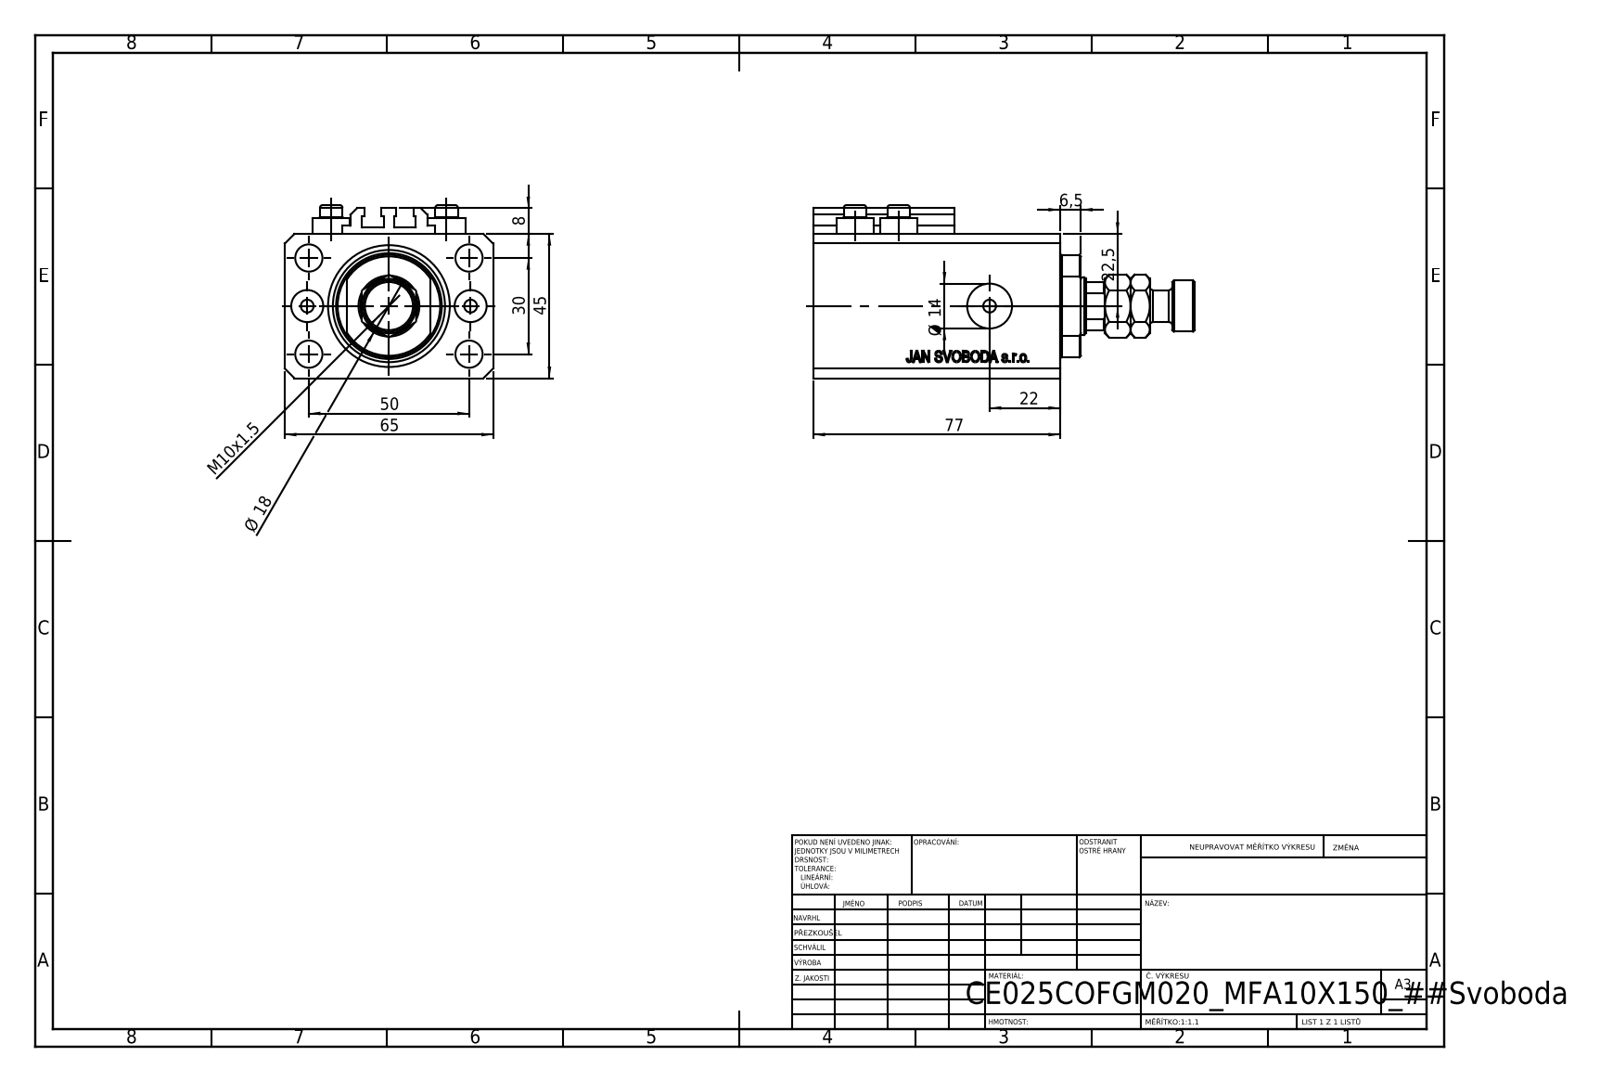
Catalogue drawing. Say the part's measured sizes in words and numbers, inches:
The part is named "ALLEN BOLT V250CE; V250CE_VC_C; V250CE_C_Body; MFA (+1 more)". Its 3-D file was written by "SolidWorks 2019 (CONFIG_CONTROL_DESIGN)". It is 9 solids with 1086 faces: 520 planar, 90 cylindrical and 476 other. Overall it measures 4.685 by 2.559 by 2.126 inches. Its volume is 13.26 cubic inches and its surface area 91.96 square inches. Round holes: 8 of diameter 0.157, 5 of diameter 0.335, 2 of diameter 0.394, 2 of diameter 0.551, 1 of diameter 0.709, 1 of diameter 0.984, 1 of diameter 1.496. Round bosses or shafts: 4 of diameter 0.457, 4 of diameter 0.276, 1 of diameter 0.63, 1 of diameter 0.394. Partial cylindrical surfaces (rounded edges, fillets, slot ends): 10 of radius 0.008, 1 of radius 0.335, 1 of radius 0.63. The main face-to-face distances are 1.772, 2.559, 0.551, 2.48, 3.031, 0.272, 2.209, 2.76, 0.807, 0.118. The hole center spacings are 0.591, 1.148, 2.074, 0.535, 1.004, 1.181, 1.417, 1.515.
